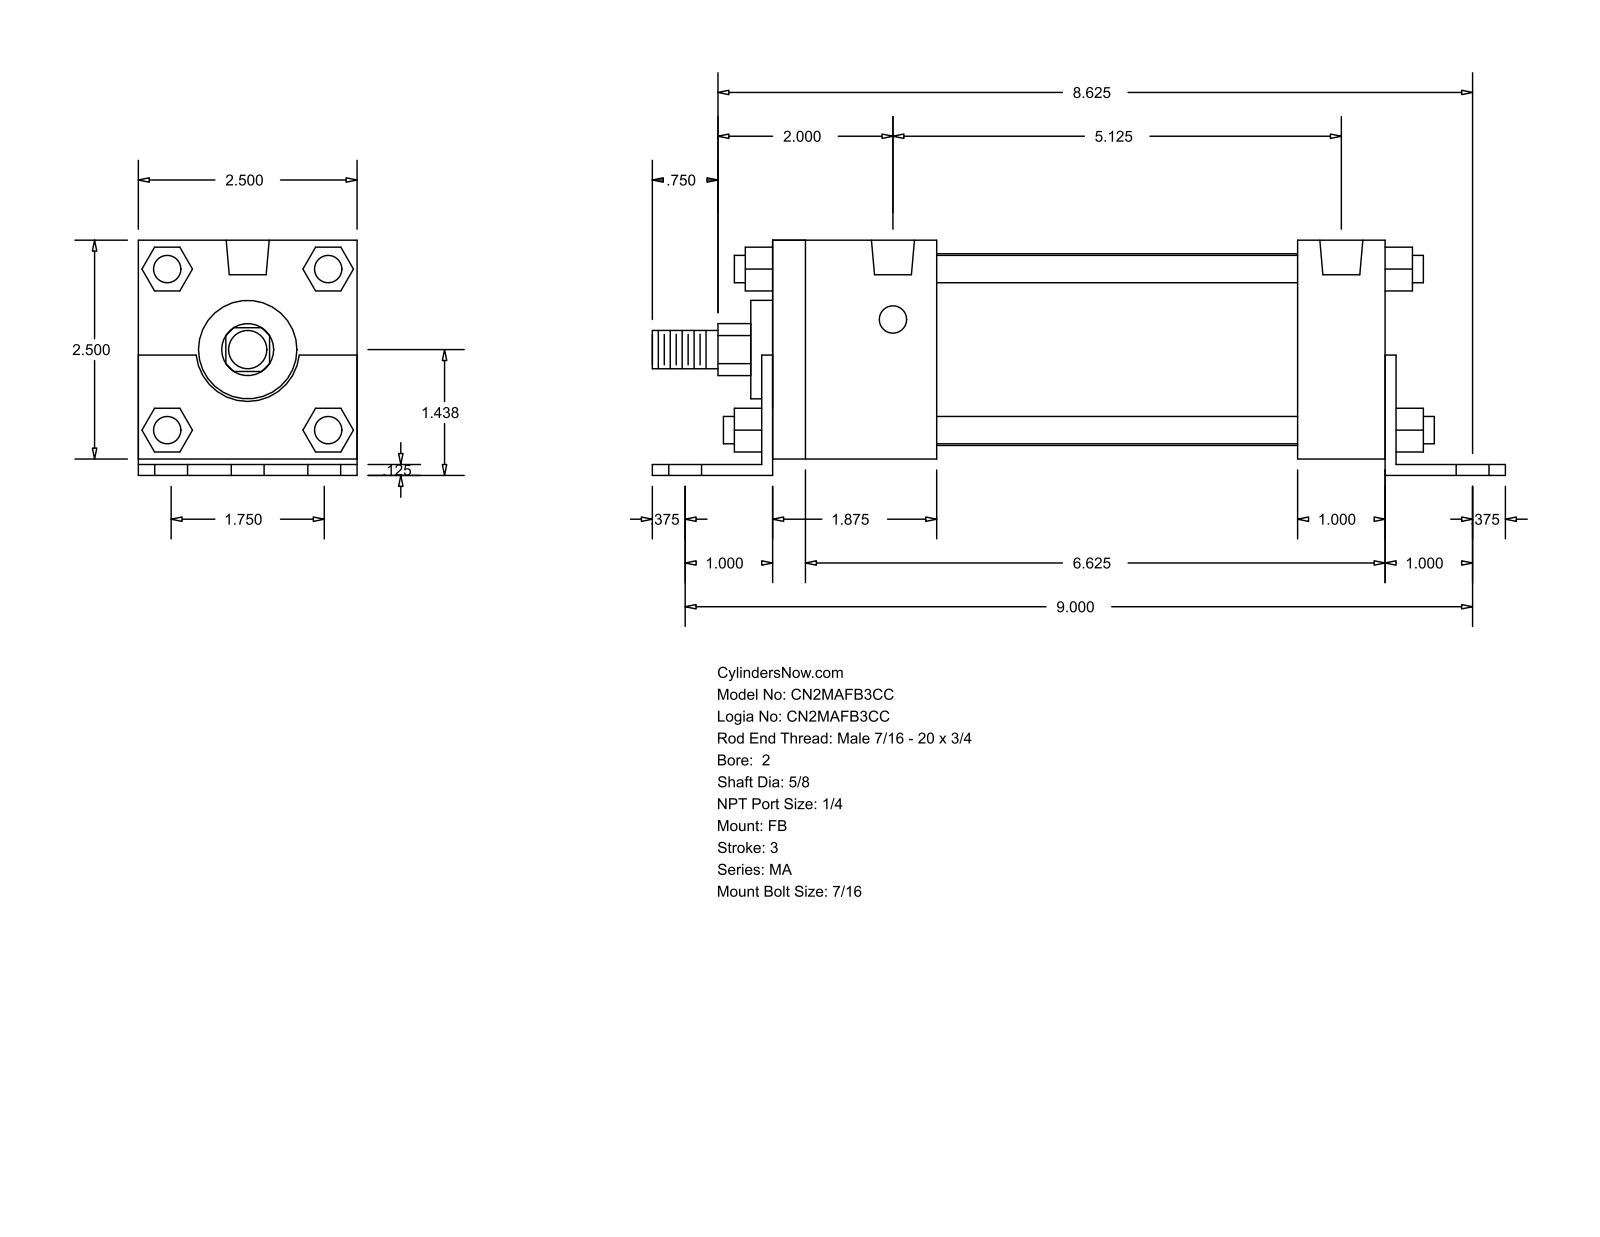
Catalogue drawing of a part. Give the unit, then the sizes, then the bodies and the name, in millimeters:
Units: millimetres
Overall size (bounding box): 247.65 × 68.26 × 63.5
Round holes (diameter × count): ⌀11.11 ×6, ⌀7.94 ×4, ⌀12.49 ×2
Round bosses / shafts (diameter × count): ⌀7.94 ×4, ⌀55.63 ×1, ⌀28.57 ×1, ⌀15.88 ×1, ⌀11.11 ×1
Partial cylindrical surfaces — rounded edges, fillets, slot ends (radius × count): R7.54 ×1, R15.05 ×1
Main face-to-face distances: 63.5, 3.17, 4.76, 68.26, 1.59, 65.09, 184.15, 3.18, 177.8, 180.97
Hole centre spacings: 22.23, 229.68, 228.6, 44.11, 44.46, 64.3, 130.17, 169.73
Bodies: 0 solids, 140 faces (105 planar, 35 cylindrical, 0 other)
Part name (STEP PRODUCT): MA_FB__0200_0.625
STEP written by: GSSL Pune (CONFIG_CONTROL_DESIGN)
